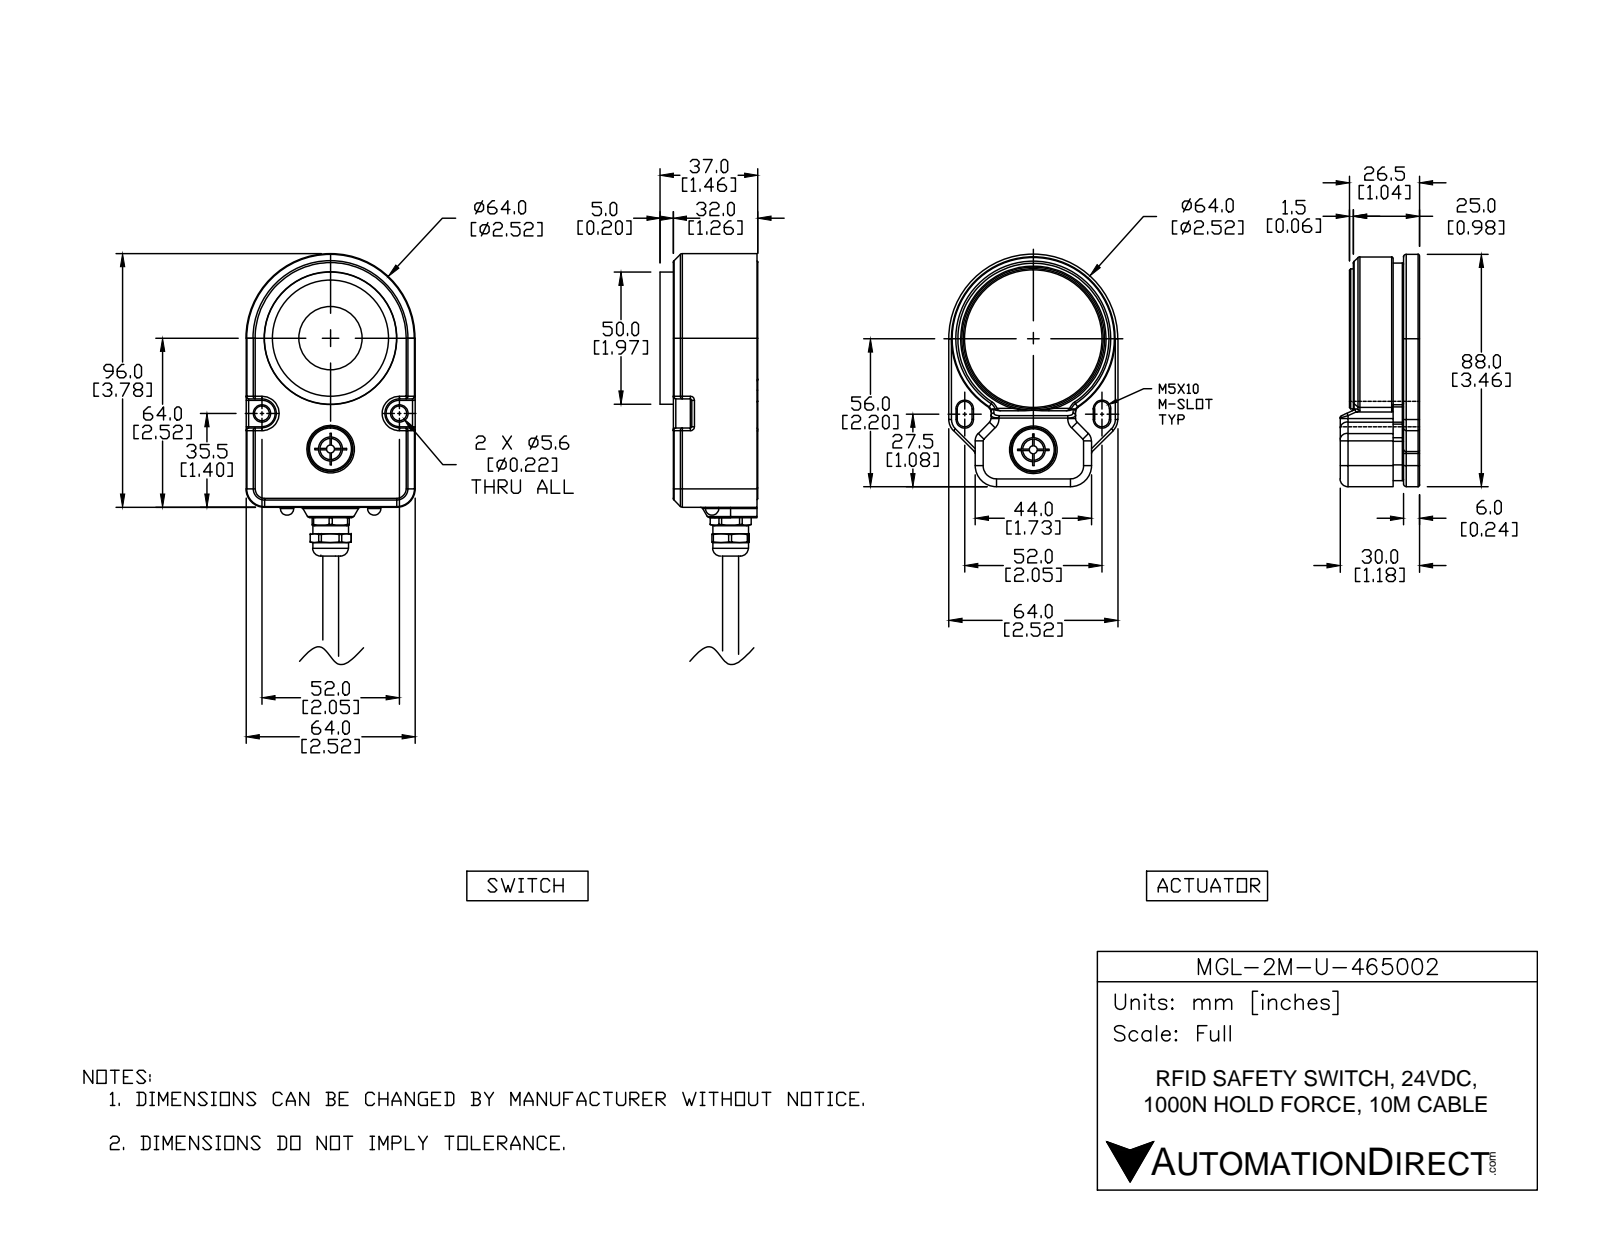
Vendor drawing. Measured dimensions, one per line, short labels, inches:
name: MGL-2M-U-465002_2; MGL-2M-U-465002; MGL-2M-U-465002_1
written by: SolidWorks 2017 (AUTOMOTIVE_DESIGN)
unit: in
bodies: 20 solids, 1852 faces (454 planar, 786 cylindrical, 612 other)
size: 7.717 × 2.539 × 2.52
volume: 12.42 in³; area: 169.6 in²
holes: 8× ⌀0.098, 8× ⌀0.157, 6× ⌀0.13, 6× ⌀0.315, 5× ⌀0.197, 3× ⌀0.323, 2× ⌀0.22, 2× ⌀0.354, 2× ⌀0.374, 2× ⌀0.413, 2× ⌀0.669, 1× ⌀0.252
bosses: 4× ⌀0.02, 3× ⌀0.079, 2× ⌀0.236, 2× ⌀0.228, 2× ⌀0.213, 1× ⌀2.441, 1× ⌀2.26, 1× ⌀2.087
rounds: 216× R0.02, 87× R0.039, 30× R0.079, 17× R0.012, 15× R0.118, 9× R0.157, 7× R0.024, 6× R0.177
face distances: 0.236, 0.413, 0.118, 0.748, 1.89, 2.303, 1.043, 0.394, 0.354, 1.142
hole spacings: 0.706, 0.768, 1.086, 1.024, 0.346, 0.376, 0.382, 0.384
